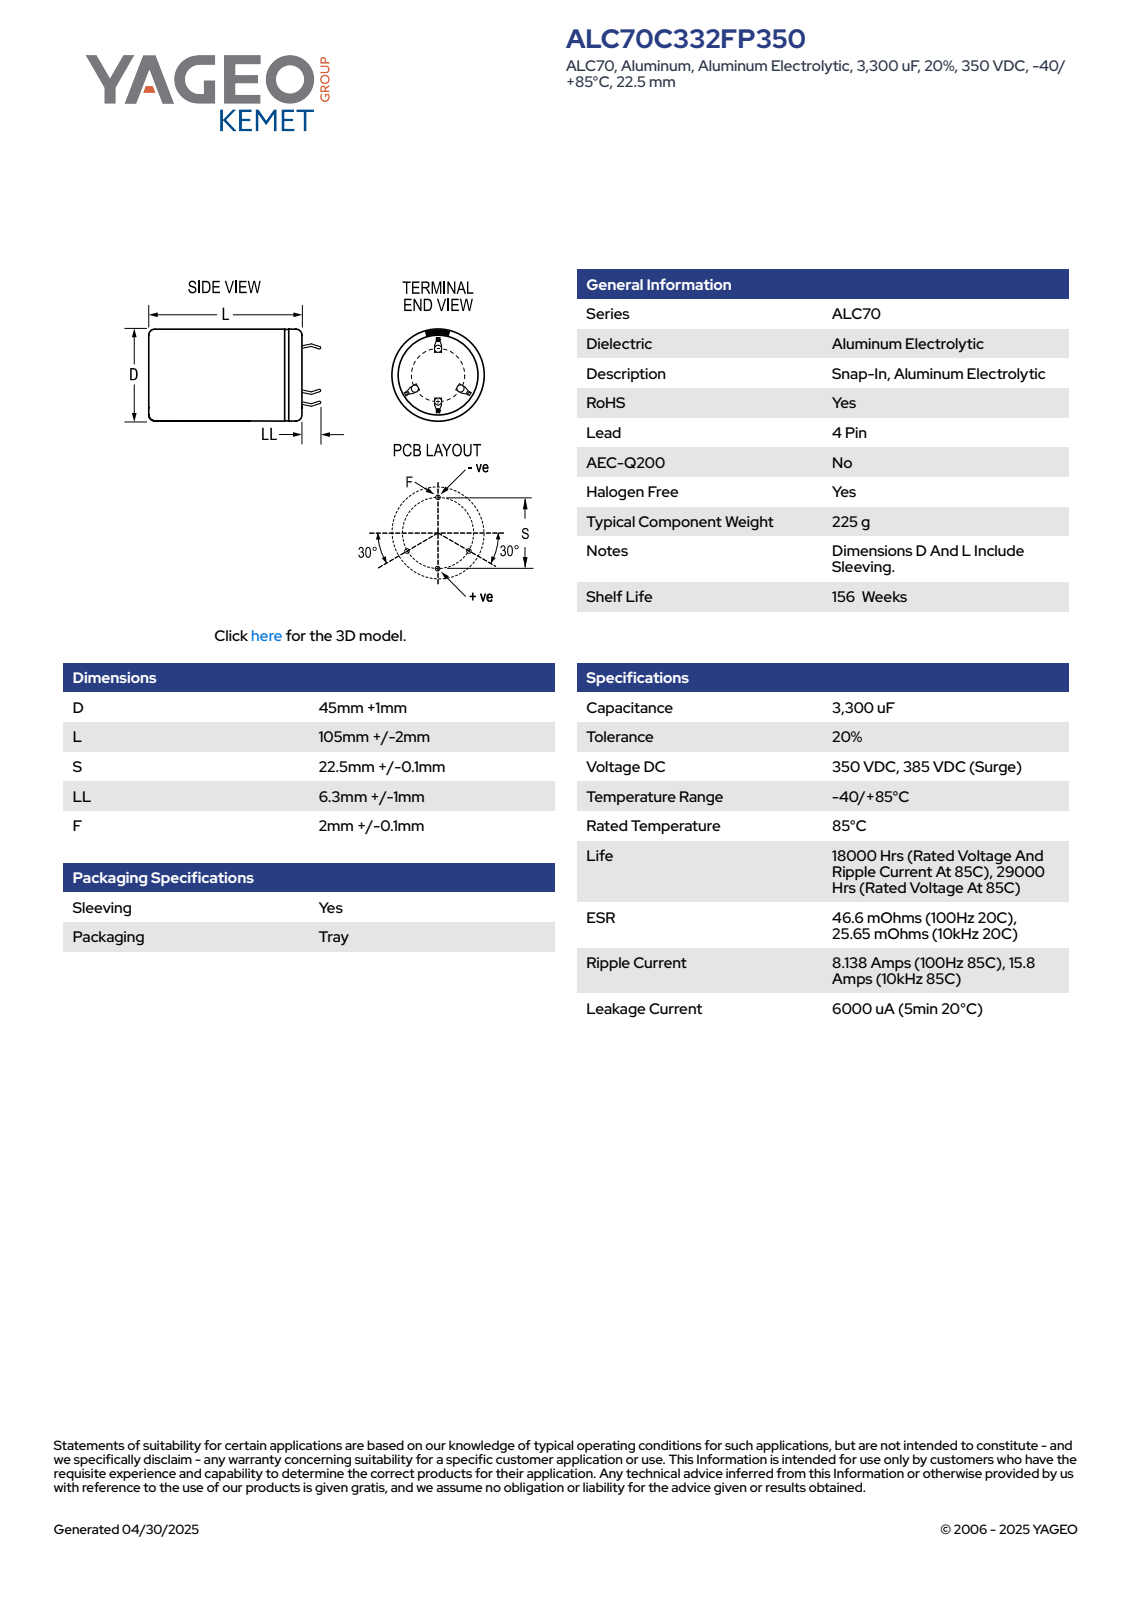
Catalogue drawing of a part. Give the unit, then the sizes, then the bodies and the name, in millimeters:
Units: millimetres
Overall size (bounding box): 114.29 × 46 × 46
Round holes (diameter × count): ⌀40.7 ×1
Round bosses / shafts (diameter × count): ⌀46 ×1
Partial cylindrical surfaces — rounded edges, fillets, slot ends (radius × count): R22.99 ×1
Main face-to-face distances: 106.99, 107.49, 0.5, 0.6, 0.31, 0.75, 1.35, 16.92, 17.22, 17.23
Volume: 176 725 mm³ · Surface area: 18 830 mm²
Bodies: 1 solid, 134 faces (80 planar, 15 cylindrical, 39 other)
Part name (STEP PRODUCT): CARS_K4P_45X105_D46L107S22.5LL7.3F2.1
STEP written by: SolidWorks 2014 (AUTOMOTIVE_DESIGN)
